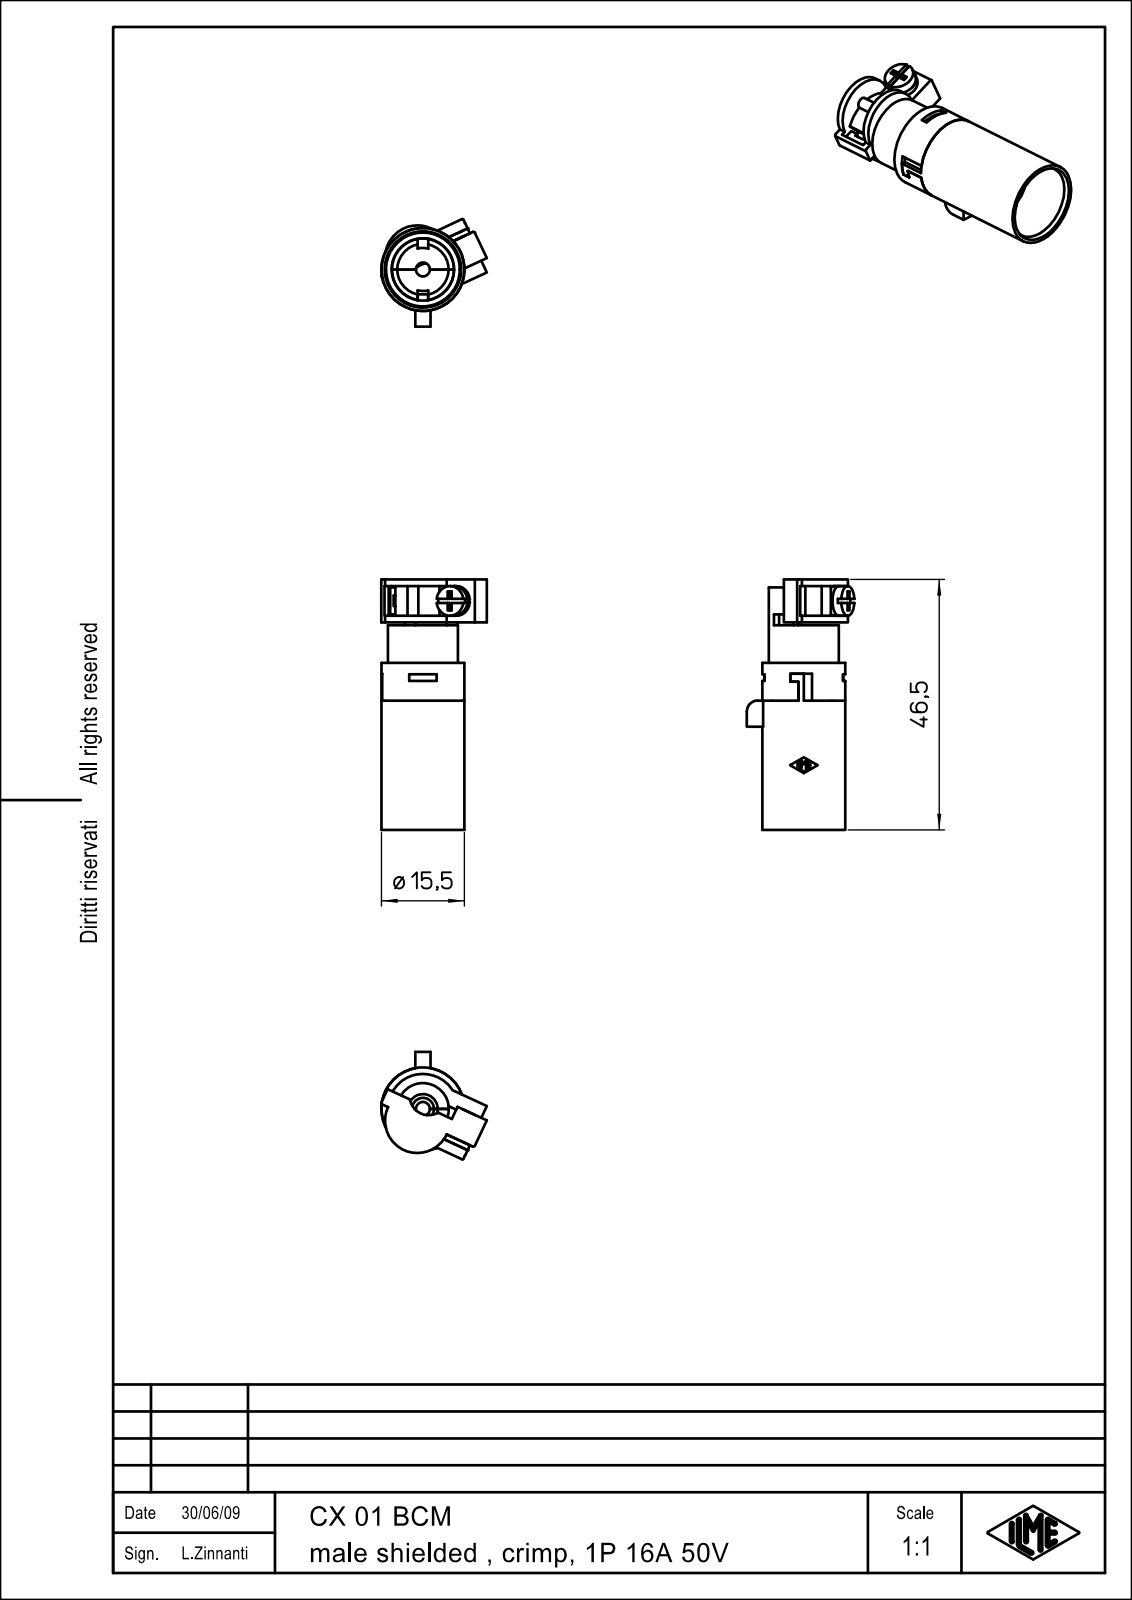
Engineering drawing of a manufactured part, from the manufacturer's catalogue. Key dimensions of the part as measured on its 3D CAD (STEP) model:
Part name (STEP PRODUCT): CX_01_BCM
STEP written by: CoCreate Modeling 16.00A 16-Aug-2008 (C) Parametric Technology GmbH (AUTOMOTIVE_DESIGN)
Units: millimetres
Bodies: 1 solid, 211 faces (89 planar, 70 cylindrical, 52 other)
Overall size (bounding box): 46.5 × 19.97 × 19.57
Volume: 4 691 mm³ · Surface area: 5 603 mm²
Round holes (diameter × count): ⌀2.6 ×1, ⌀3.2 ×1, ⌀4.1 ×1, ⌀4.5 ×1, ⌀5.5 ×1, ⌀9.6 ×1, ⌀13.7 ×1
Round bosses / shafts (diameter × count): ⌀15.4 ×1, ⌀13 ×1, ⌀11.6 ×1, ⌀11.5 ×1, ⌀5.5 ×1, ⌀3 ×1, ⌀2.5 ×1
Partial cylindrical surfaces — rounded edges, fillets, slot ends (radius × count): R0.2 ×4, R0.5 ×3, R0.3 ×2, R4 ×2, R1 ×1, R2 ×1, R3.5 ×1, R5.3 ×1
Main face-to-face distances: 8, 1.25, 6.75, 7, 5.5, 2, 1.5, 6.5, 8.5, 5.25
